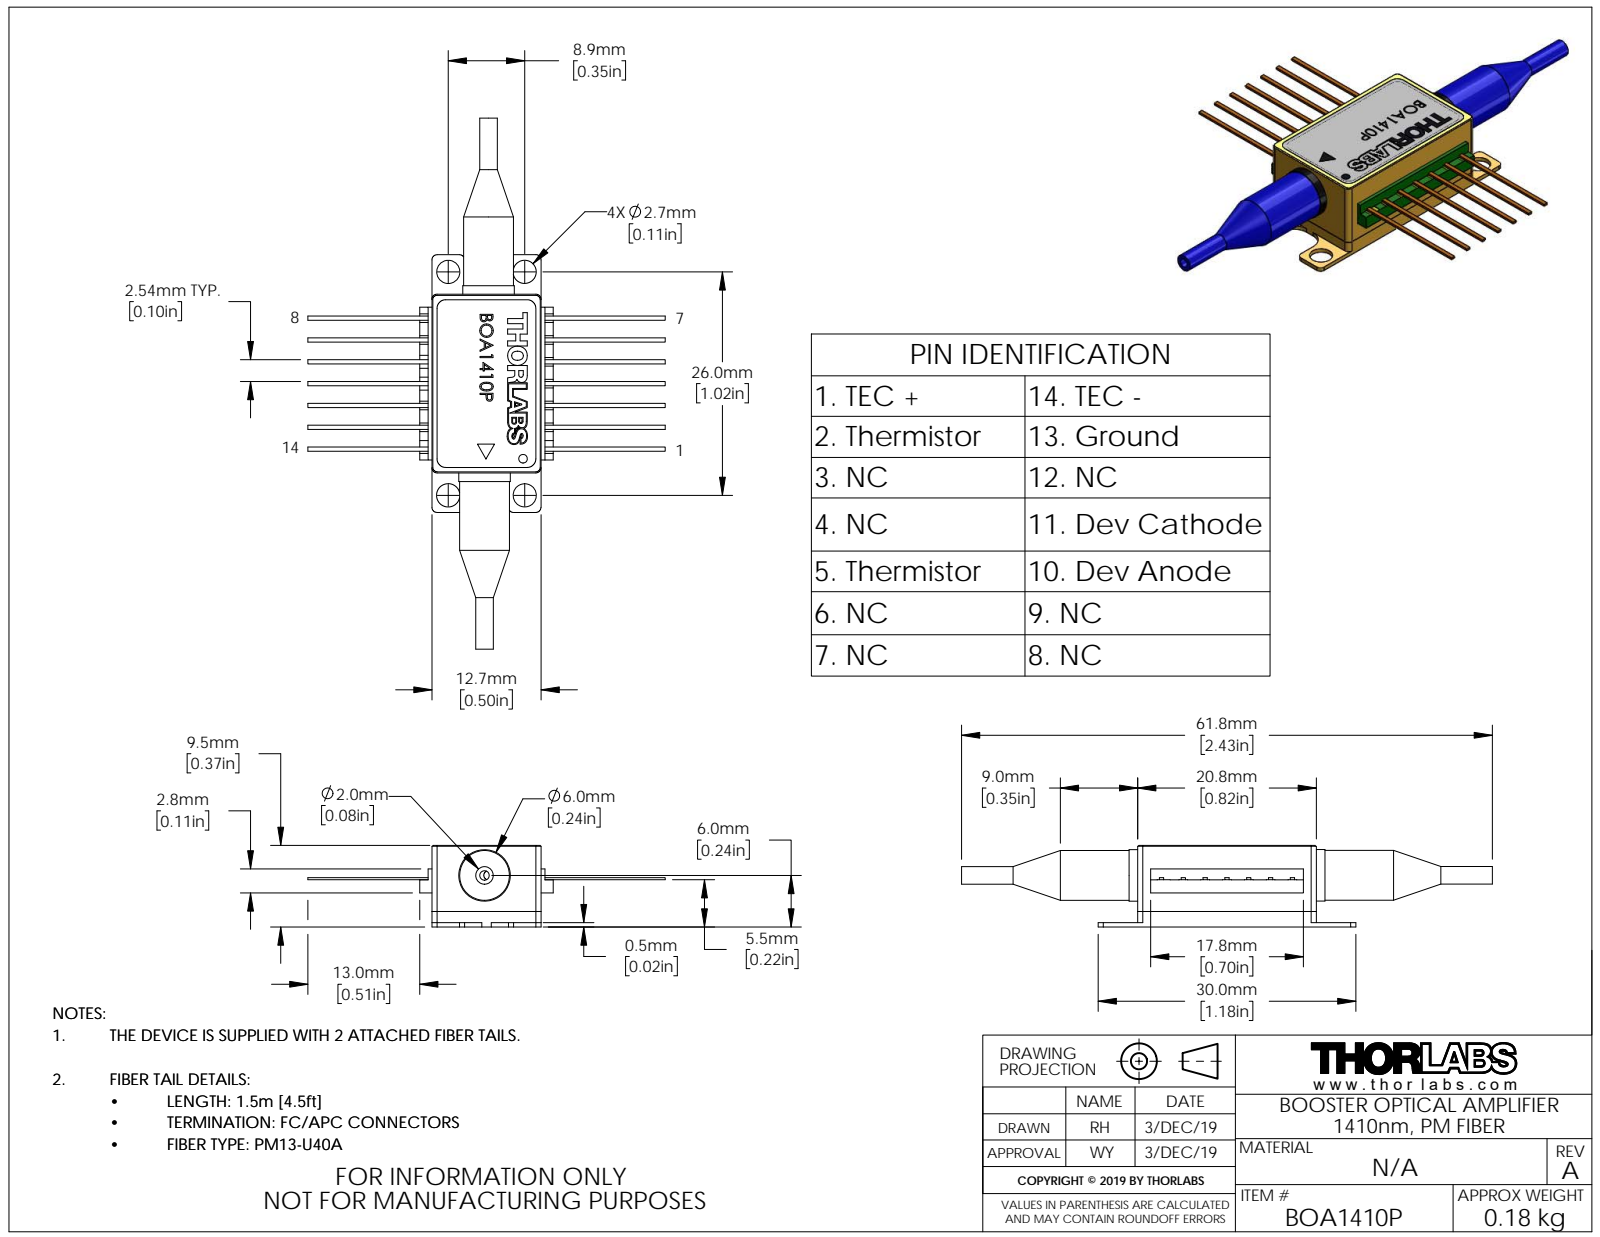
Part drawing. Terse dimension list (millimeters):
name: QTN039250-E0W
written by: SolidWorks 2018 (AUTOMOTIVE_DESIGN)
unit: mm
bodies: 0 solids, 352 faces (255 planar, 51 cylindrical, 46 other)
size: 61.8 × 41.6 × 9.5
holes: 4× ⌀2.7, 2× ⌀1.1, 1× ⌀1
bosses: 2× ⌀6, 2× ⌀5.8, 2× ⌀2.04
rounds: 12× R0.6, 4× R0.5, 4× R2, 1× R1
face distances: 9.48, 12.7, 1.8, 7.68, 1.52, 3.69, 5.49, 3.99, 2.17, 3.97
hole spacings: 8.9, 26, 27.48, 0.47, 4.27, 9.69, 21.73, 23.41
